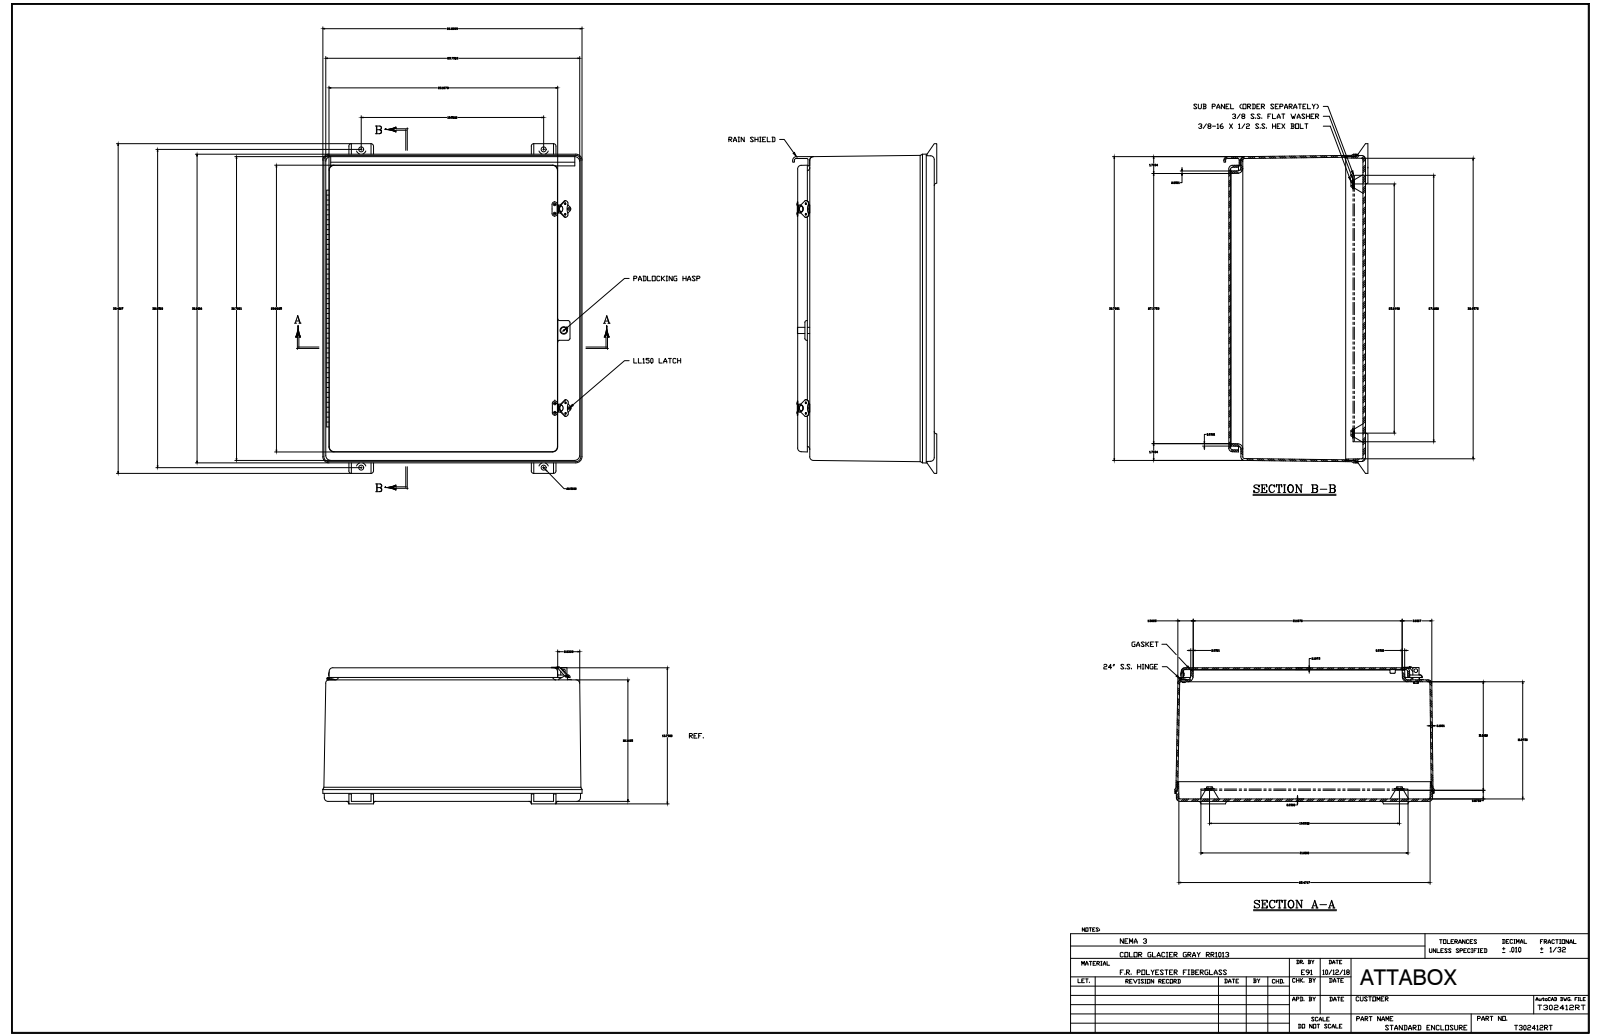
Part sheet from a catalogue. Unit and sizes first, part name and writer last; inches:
Units: inches
Overall size (bounding box): 33.406 × 26.281 × 14.313
Round holes (diameter × count): ⌀0.13 ×21, ⌀0.063 ×8, ⌀0.1 ×8, ⌀0.201 ×8, ⌀0.138 ×4, ⌀0.187 ×4, ⌀0.563 ×4, ⌀0.065 ×2, ⌀0.281 ×2, ⌀0.51 ×2, ⌀0.51 ×2, ⌀0.065 ×1
Round bosses / shafts (diameter × count): ⌀0.357 ×8, ⌀0.187 ×8, ⌀0.14 ×8, ⌀0.297 ×3, ⌀0.5 ×2, ⌀0.25 ×1, ⌀0.201 ×1, ⌀0.2 ×1
Partial cylindrical surfaces — rounded edges, fillets, slot ends (radius × count): R0.01 ×60, R0.25 ×24, R0.312 ×14, R0.187 ×12, R0.375 ×12, R0.5 ×12, R0.188 ×10, R0.016 ×8
Main face-to-face distances: 0.187, 0.25, 0.188, 13.531, 13.281, 13.343, 13.093, 12.312, 1.219, 1.031
Hole centre spacings: 7.5, 3.489, 15.5, 20.187, 24.444, 25.381, 28.707, 29.106
Volume: 693.1 in³ · Surface area: 7 081 in²
Bodies: 40 solids, 1219 faces (479 planar, 486 cylindrical, 254 other)
Part name (STEP PRODUCT): T302412RT
STEP written by: SolidWorks 2018 (AUTOMOTIVE_DESIGN)
